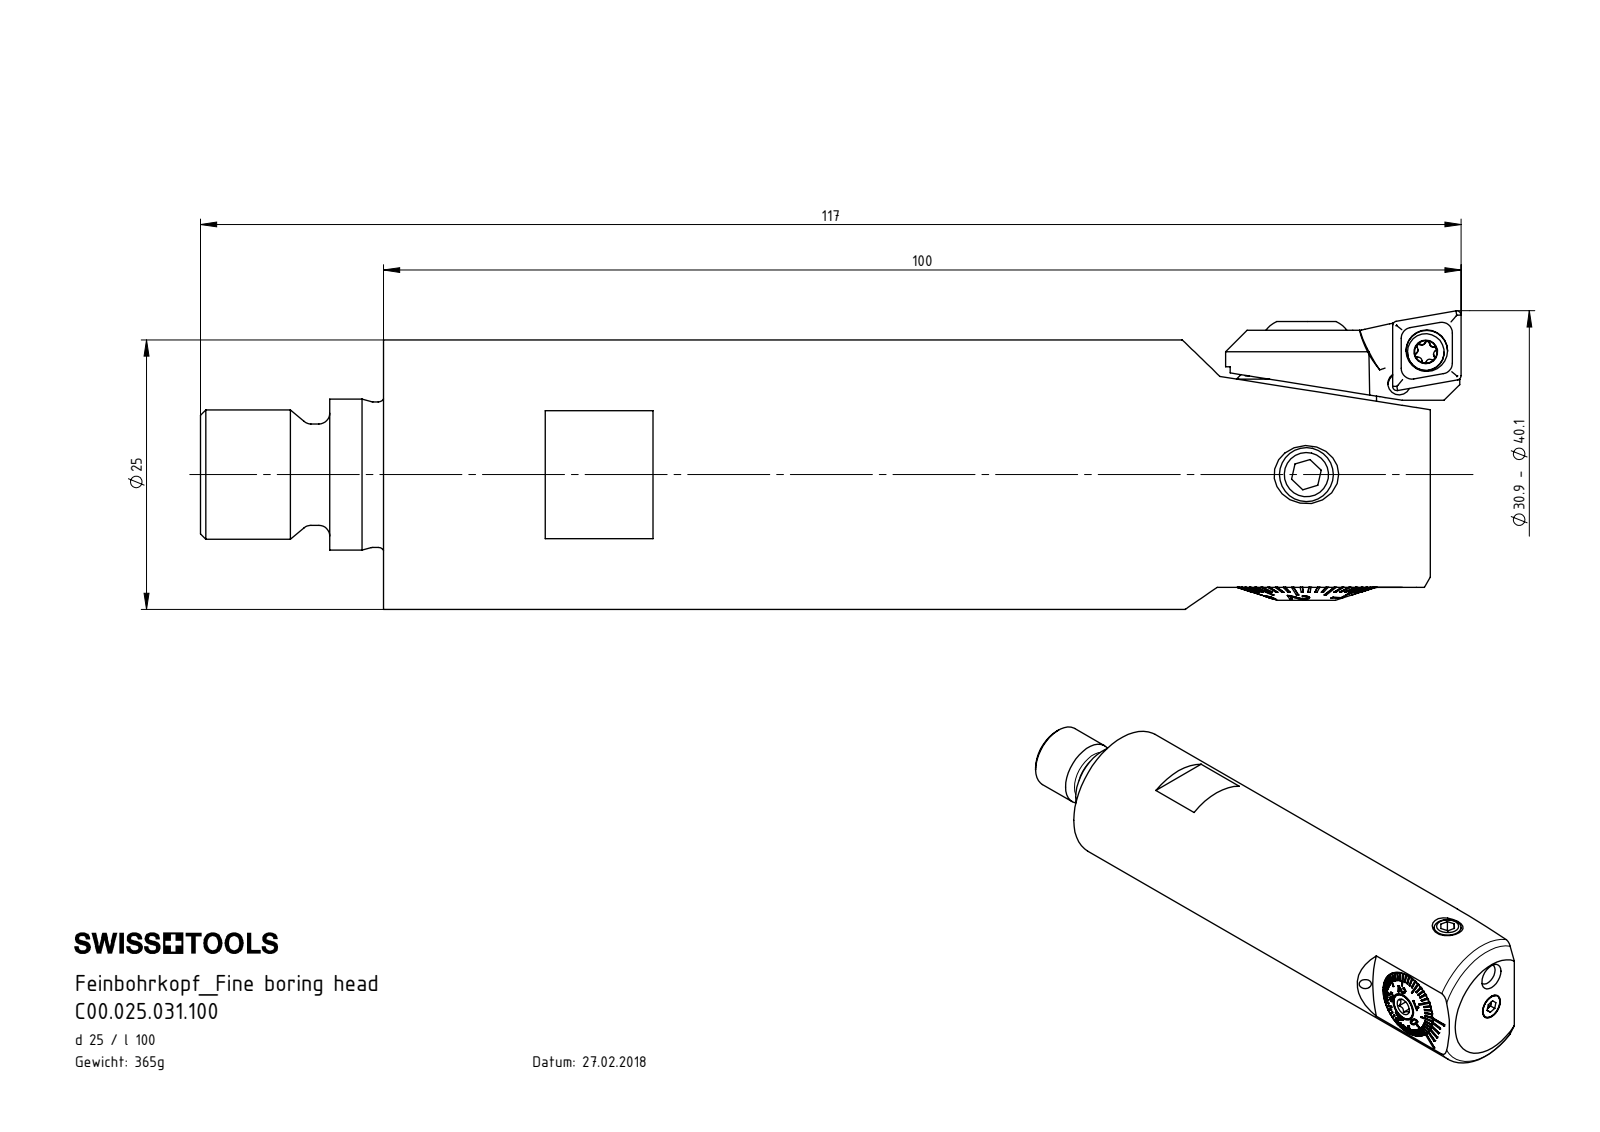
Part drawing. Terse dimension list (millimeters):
name: HP2-F25.K20.100_C; F25-BG1.002.013_C; F25-BG2.010.011_A; F25-BG2.013.003_A (+8 more)
written by: SolidWorks 2017 (CONFIG_CONTROL_DESIGN)
unit: mm
bodies: 16 solids, 790 faces (347 planar, 146 cylindrical, 297 other)
size: 117 × 27.7 × 25
volume: 46 483 mm³; area: 16 811 mm²
holes: 4× ⌀2, 2× ⌀2.05, 2× ⌀4.2, 2× ⌀5, 1× ⌀2.1, 1× ⌀2.4, 1× ⌀2.7, 1× ⌀2.8, 1× ⌀3, 1× ⌀3.85, 1× ⌀5.5, 1× ⌀6.4
bosses: 2× ⌀5, 2× ⌀4.95, 2× ⌀2.5, 1× ⌀25, 1× ⌀14, 1× ⌀13.5, 1× ⌀12.98, 1× ⌀12.85
rounds: 6× R0.21, 5× R0.36, 4× R0.5, 2× R1.32, 1× R0.2, 1× R0.36, 1× R1.05, 1× R1.25
face distances: 97.15, 1.5, 19.95, 3.1, 15.7, 0.8, 19.6, 3.9, 22, 18.8
hole spacings: 3.84, 4, 4.08, 6.8, 8.9
